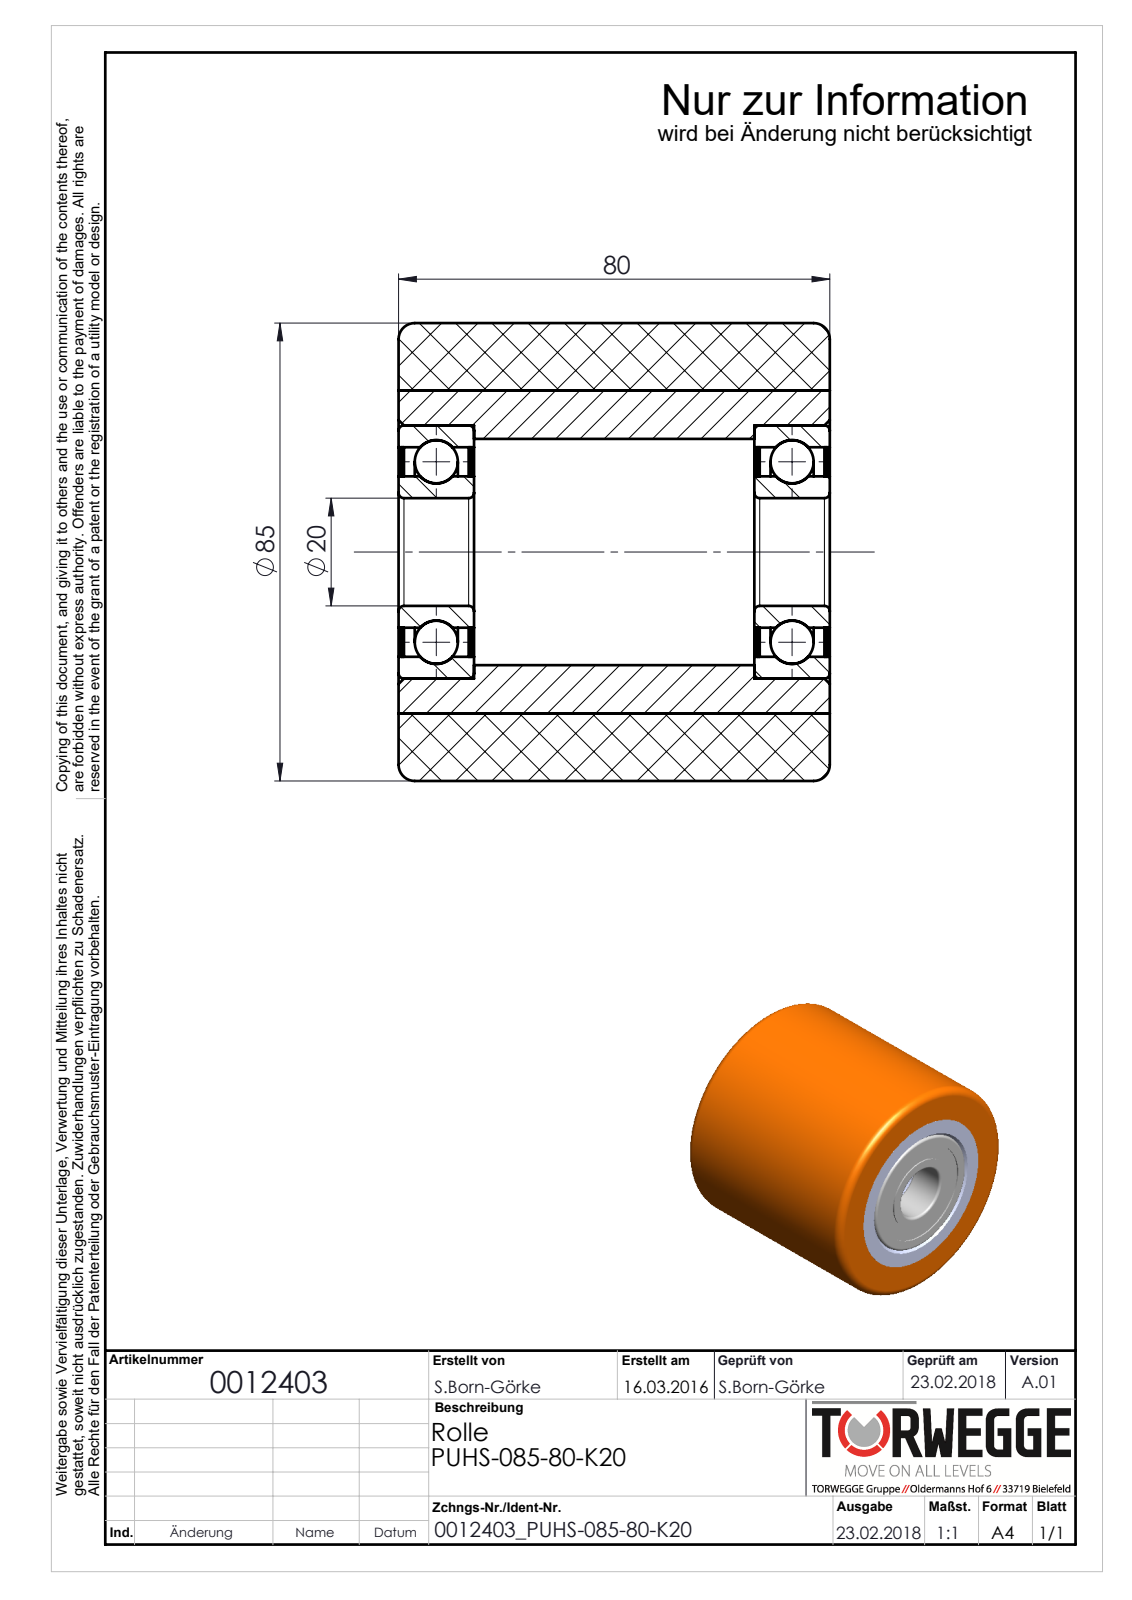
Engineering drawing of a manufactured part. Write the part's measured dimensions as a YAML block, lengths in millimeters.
part_name: "0012403_PUHS-085-80-K20"
step_written_by: "SolidWorks 2016 (AUTOMOTIVE_DESIGN)"
units: millimeters
bodies: {solids: 12, faces: 118, planar: 22, cylindrical: 52, other: 44}
overall_size: [85, 85, 80]
volume: 365057
surface_area: 95666
round_holes:
  - {diameter: 20, count: 1}
  - {diameter: 28.1, count: 1}
  - {diameter: 38.9, count: 1}
  - {diameter: 42, count: 1}
  - {diameter: 47, count: 1}
  - {diameter: 60, count: 1}
round_bosses_or_shafts:
  - {diameter: 85, count: 1}
face_to_face_distances: [0.5, 66, 80, 13, 1, 13.5, 66.5, 12.5, 65.5, 14]
